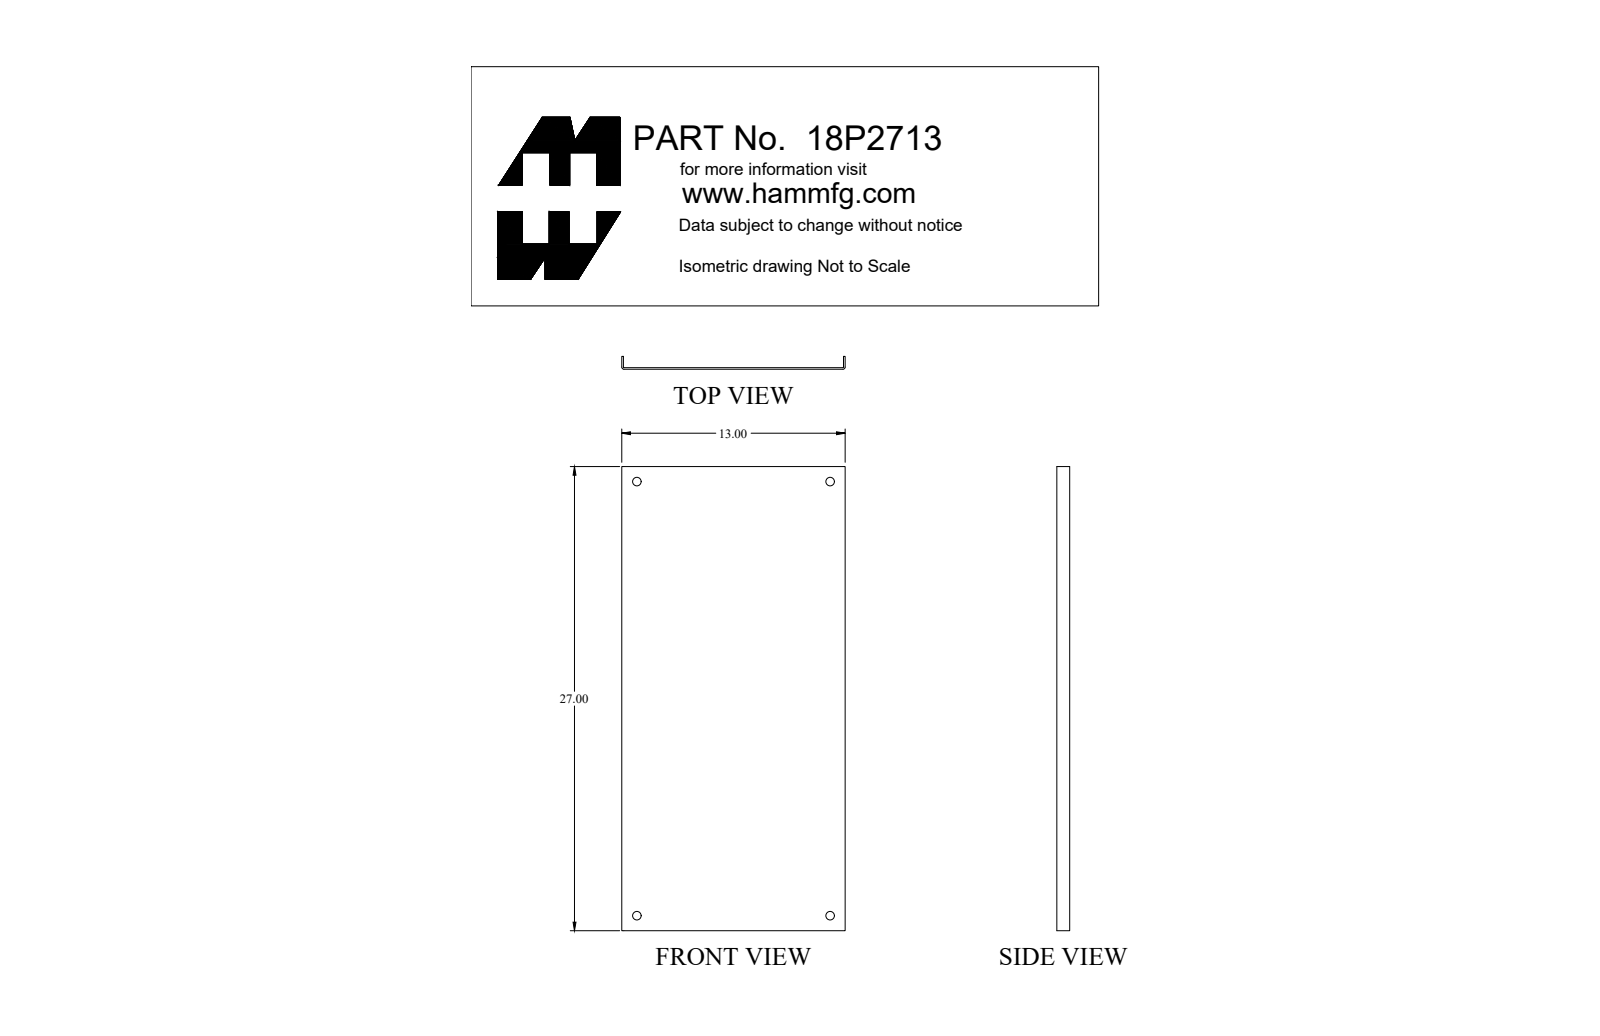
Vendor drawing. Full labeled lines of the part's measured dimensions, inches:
Part name (STEP PRODUCT): 18P2713_Default
STEP written by: SolidWorks 2018 (CONFIG_CONTROL_DESIGN)
Units: inches
Bodies: 1 solid, 22 faces (10 planar, 12 cylindrical, 0 other)
Overall size (bounding box): 27 × 13 × 0.75
Volume: 36.46 in³ · Surface area: 776 in²
Round holes (diameter × count): ⌀0.5 ×4
Partial cylindrical surfaces — rounded edges, fillets, slot ends (radius × count): R0.03 ×2, R0.125 ×2
Main face-to-face distances: 0.095, 12.905, 13, 12.81, 0.75, 0.655, 27
Hole centre spacings: 11.25, 25.25, 27.643
